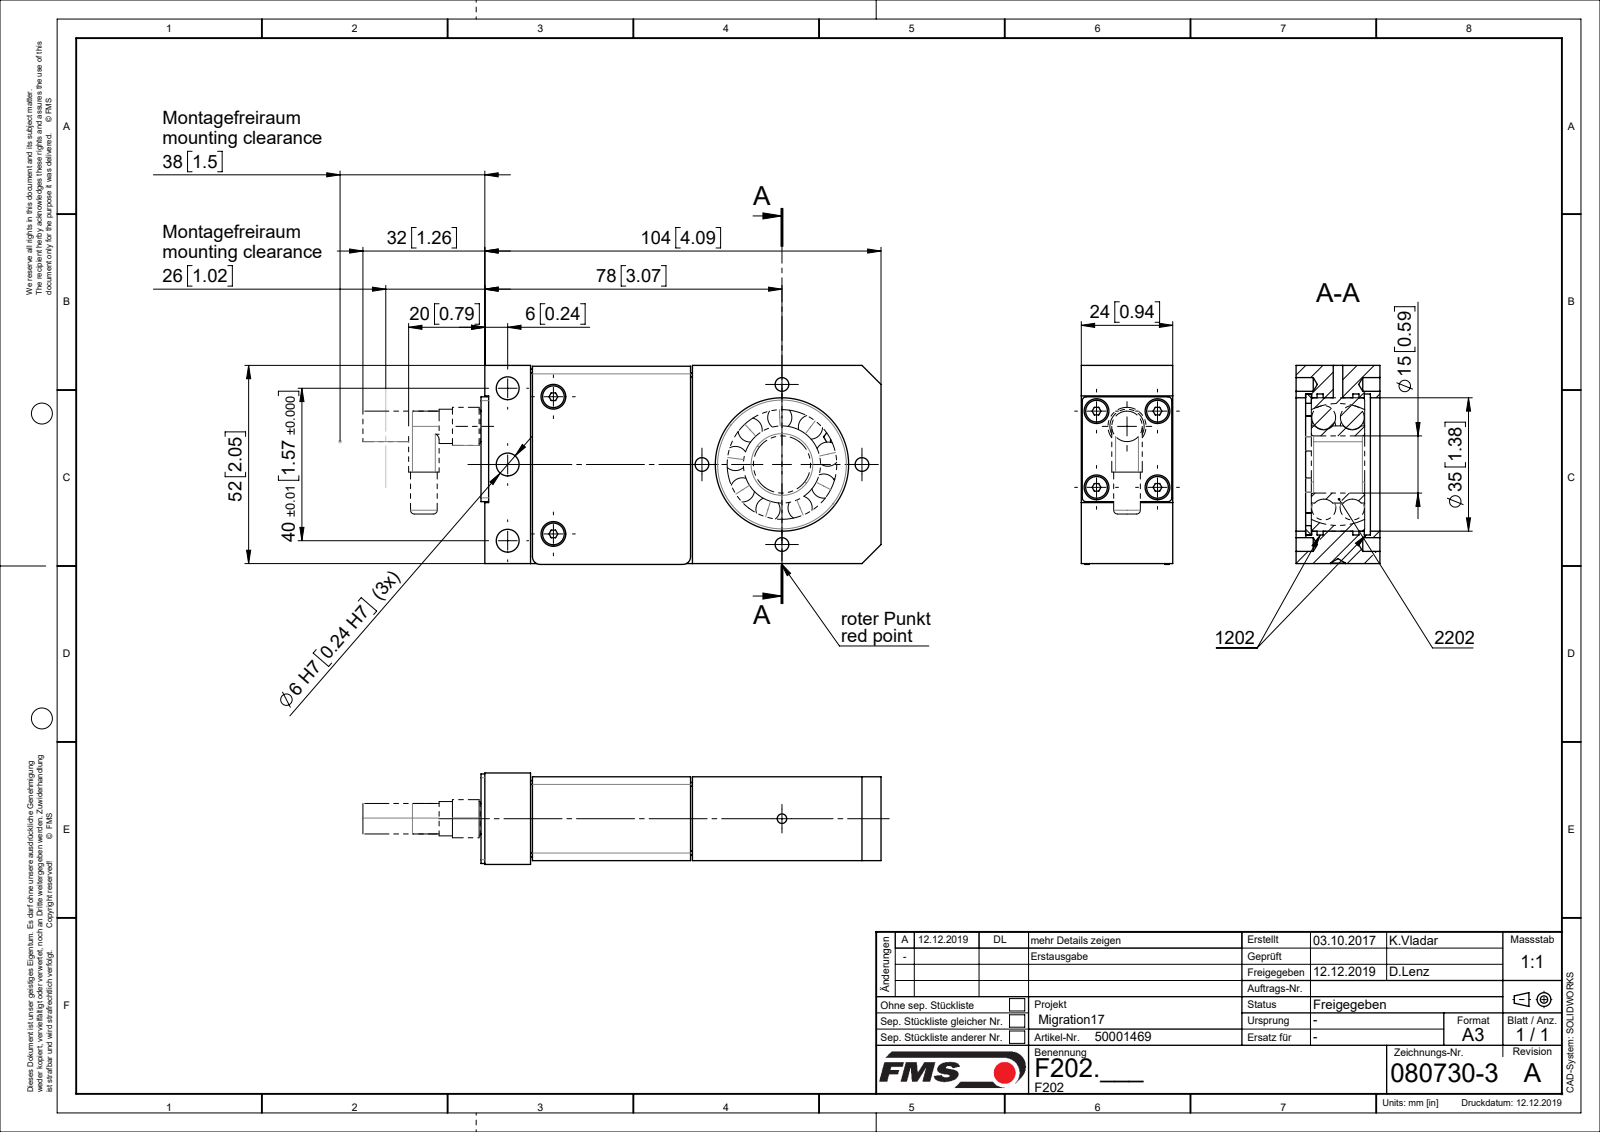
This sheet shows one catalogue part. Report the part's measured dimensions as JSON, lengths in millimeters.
{"part_name": "F0807303C; F0807304; F0807305; SENKSCHRAUBE_I-6KT_M3X6 (+6 more)", "step_written_by": "Mechanical Desktop 2009 (CONFIG_CONTROL_DESIGN)", "units": "millimeters", "bodies": {"solids": 15, "faces": 467, "planar": 180, "cylindrical": 170, "other": 117}, "overall_size": [123, 52, 24], "volume_mm3": 80558, "surface_area_mm2": 39969, "round_holes": [[2.6, 7], [1, 4], [3.2, 4], [3.6, 4], [6, 4], [4, 1], [6.5, 1], [7, 1], [10, 1], [12, 1], [35, 1], [37, 1]], "round_bosses_or_shafts": [[6, 7], [3, 6], [1, 4], [9, 1], [8, 1], [7.6, 1], [7, 1], [4, 1]], "partial_cylinders_radius": [[2, 10], [1, 6], [5, 4], [4.1, 1]], "face_to_face_distances": [1, 21, 22, 20, 1.5, 19.5, 0.5, 20.5, 52, 2], "hole_center_spacings": [2.24, 20, 21, 29.7, 2, 10, 3.61, 7.21]}
